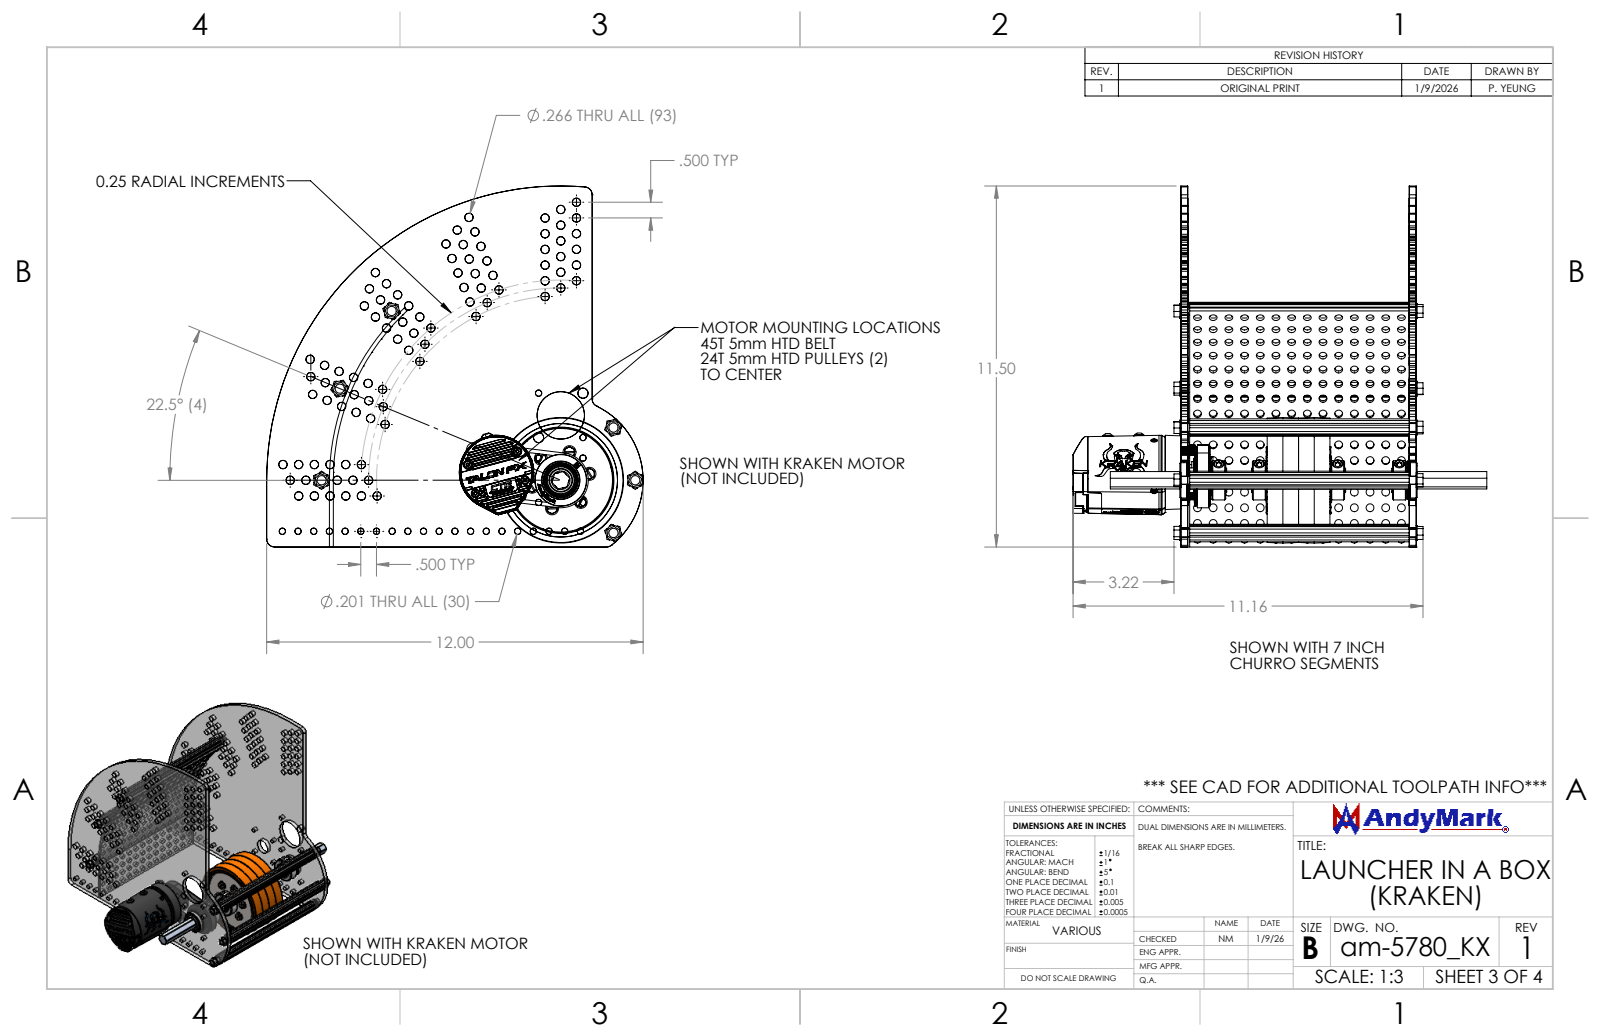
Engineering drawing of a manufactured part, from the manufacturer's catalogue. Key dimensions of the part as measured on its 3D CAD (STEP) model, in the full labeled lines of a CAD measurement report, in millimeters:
Part name (STEP PRODUCT): am-5209_45T 45T 5mm HTD 9mm Wide Belt; Stealth Wheel FlyWheel; 7IN Churro; am-1123 10-24 Hex Washer Rolling x 3-4_93882A213 (+8 more)
STEP written by: SolidWorks 2024 (AUTOMOTIVE_DESIGN)
Units: millimetres
Bodies: 60 solids, 9846 faces (1334 planar, 4060 cylindrical, 4452 other)
Overall size (bounding box): 304.8 × 304.8 × 292.1
Volume: 1 286 000 mm³ · Surface area: 653 500 mm²
Round holes (diameter × count): ⌀6.4 ×224, ⌀6.8 ×112, ⌀5.1 ×34, ⌀4 ×10, ⌀7.5 ×7, ⌀5 ×6, ⌀5.9 ×6, ⌀8.4 ×4, ⌀8.3 ×2, ⌀19.2 ×2, ⌀23.9 ×2, ⌀26 ×2
Round bosses / shafts (diameter × count): ⌀4.8 ×10, ⌀12.2 ×7, ⌀6.4 ×7, ⌀10.5 ×6, ⌀3.7 ×6, ⌀8 ×4, ⌀83.8 ×2, ⌀42 ×2
Partial cylindrical surfaces — rounded edges, fillets, slot ends (radius × count): R0.3 ×237, R0.3 ×96, R0.4 ×96, R0.4 ×96, R1.4 ×96, R1.8 ×96, R2.3 ×96, R2.8 ×96
Main face-to-face distances: 184.9, 5.6, 190.5, 179.3, 12.7, 95.3, 89.7, 3.2, 82.6, 108
Hole centre spacings: 12.7, 25.4, 38.1, 50.8, 63.5, 76.2, 88.9, 101.6
